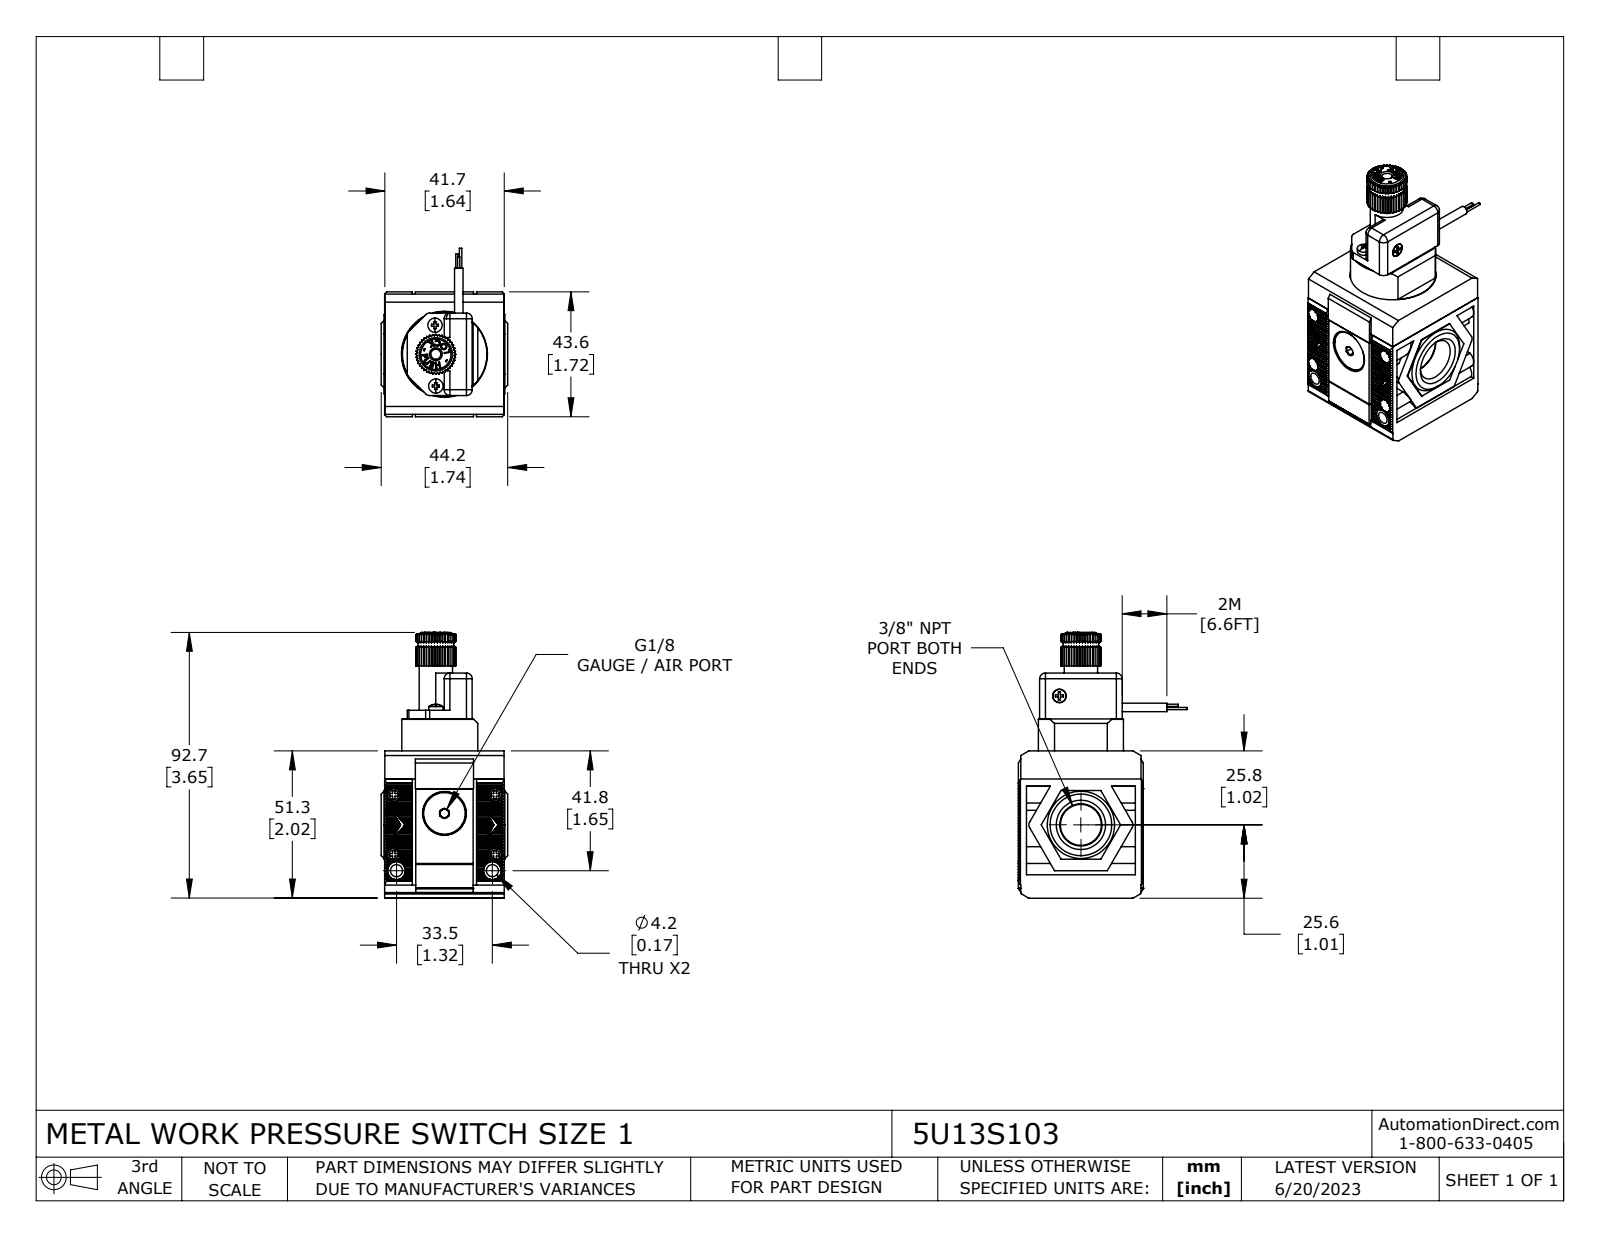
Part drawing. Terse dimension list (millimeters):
name: 5U13S103
written by: SolidWorks 2021 (CONFIG_CONTROL_DESIGN)
unit: mm
bodies: 13 solids, 1571 faces (1086 planar, 298 cylindrical, 187 other)
size: 92.8 × 58.8 × 44.2
volume: 101 800 mm³; area: 35 260 mm²
holes: 4× ⌀2.1, 4× ⌀3, 4× ⌀4.7, 2× ⌀4.2, 1× ⌀1.8, 1× ⌀8.6, 1× ⌀15.3, 1× ⌀30, 1× ⌀32
bosses: 5× ⌀4.6, 4× ⌀2.6, 3× ⌀0.8, 2× ⌀6.2, 2× ⌀5, 1× ⌀29.7, 1× ⌀22.8, 1× ⌀18.2
rounds: 14× R2, 4× R0.6, 4× R3.1, 2× R0.2, 1× R0.2, 1× R0.2, 1× R0.2, 1× R0.2
face distances: 41.6, 41.7, 42.5, 34, 7.8, 9.8, 2.8, 1.1, 0.8, 41.8
hole spacings: 5.6, 18.8, 20.9, 22.9, 26.1, 26.5, 34.9, 35.4
